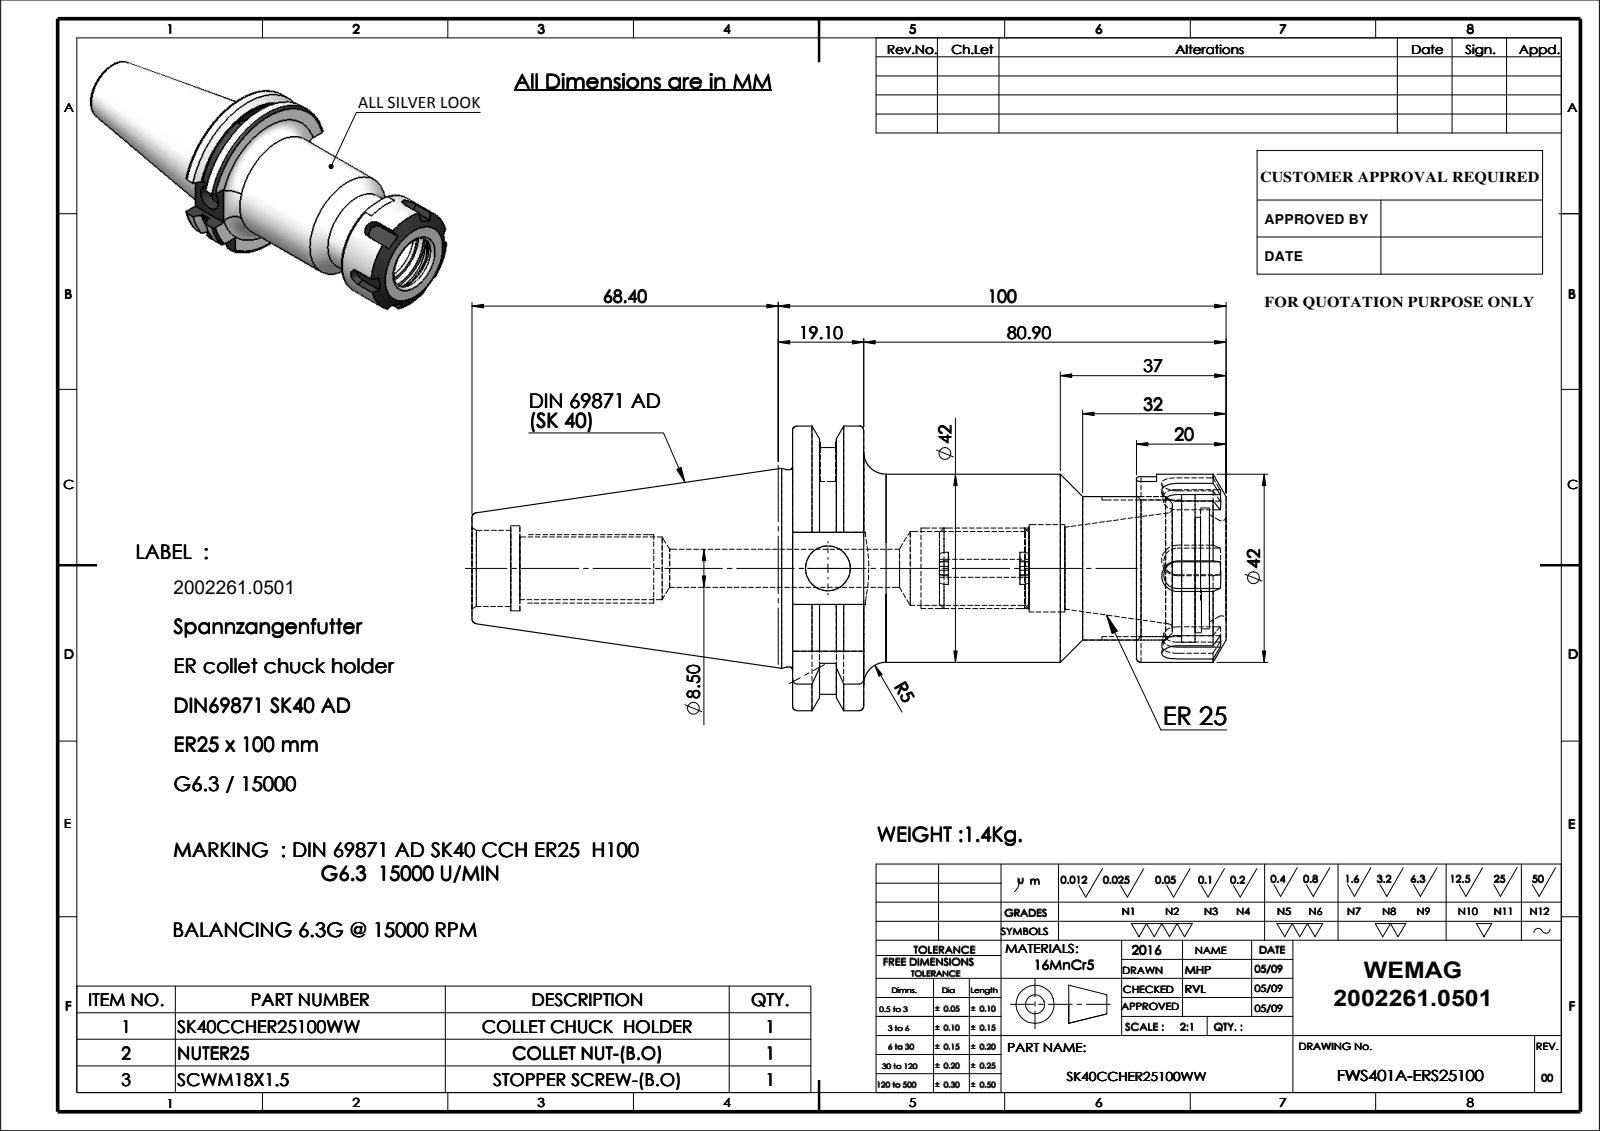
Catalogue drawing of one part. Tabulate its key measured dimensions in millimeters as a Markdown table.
| quantity | value |
| --- | --- |
| part name | 91406-ER125100; SK40CCHER25100WW; FTSCWM18X150; FTNUTER25 |
| STEP written by | SolidWorks 2009 (CONFIG_CONTROL_DESIGN) |
| units | millimeters |
| bodies | 3 solids, 185 faces (70 planar, 46 cylindrical, 69 other) |
| overall size | 168.4 × 63.55 × 61.48 |
| volume | 185 256 mm³ |
| surface area | 39 942 mm² |
| round holes (diameter × count) | 4 × 1, 8.5 × 1, 10 × 1, 14 × 1, 16.5 × 1, 17 × 1, 19 × 1, 19.5 × 1, 25.8 × 1, 27 × 1, 30.5 × 1, 33 × 1 |
| round bosses / shafts (diameter × count) | 44.05 × 1, 42 × 1, 32 × 1, 18 × 1 |
| partial cylindrical surfaces (radius × count) | 28.12 × 1, 31.77 × 1 |
| main face-to-face distances | 15.9, 60.9, 76.8, 20, 80.9, 96.8, 44, 6.9, 13.1, 74 |
| hole center spacings | 1.5 |
